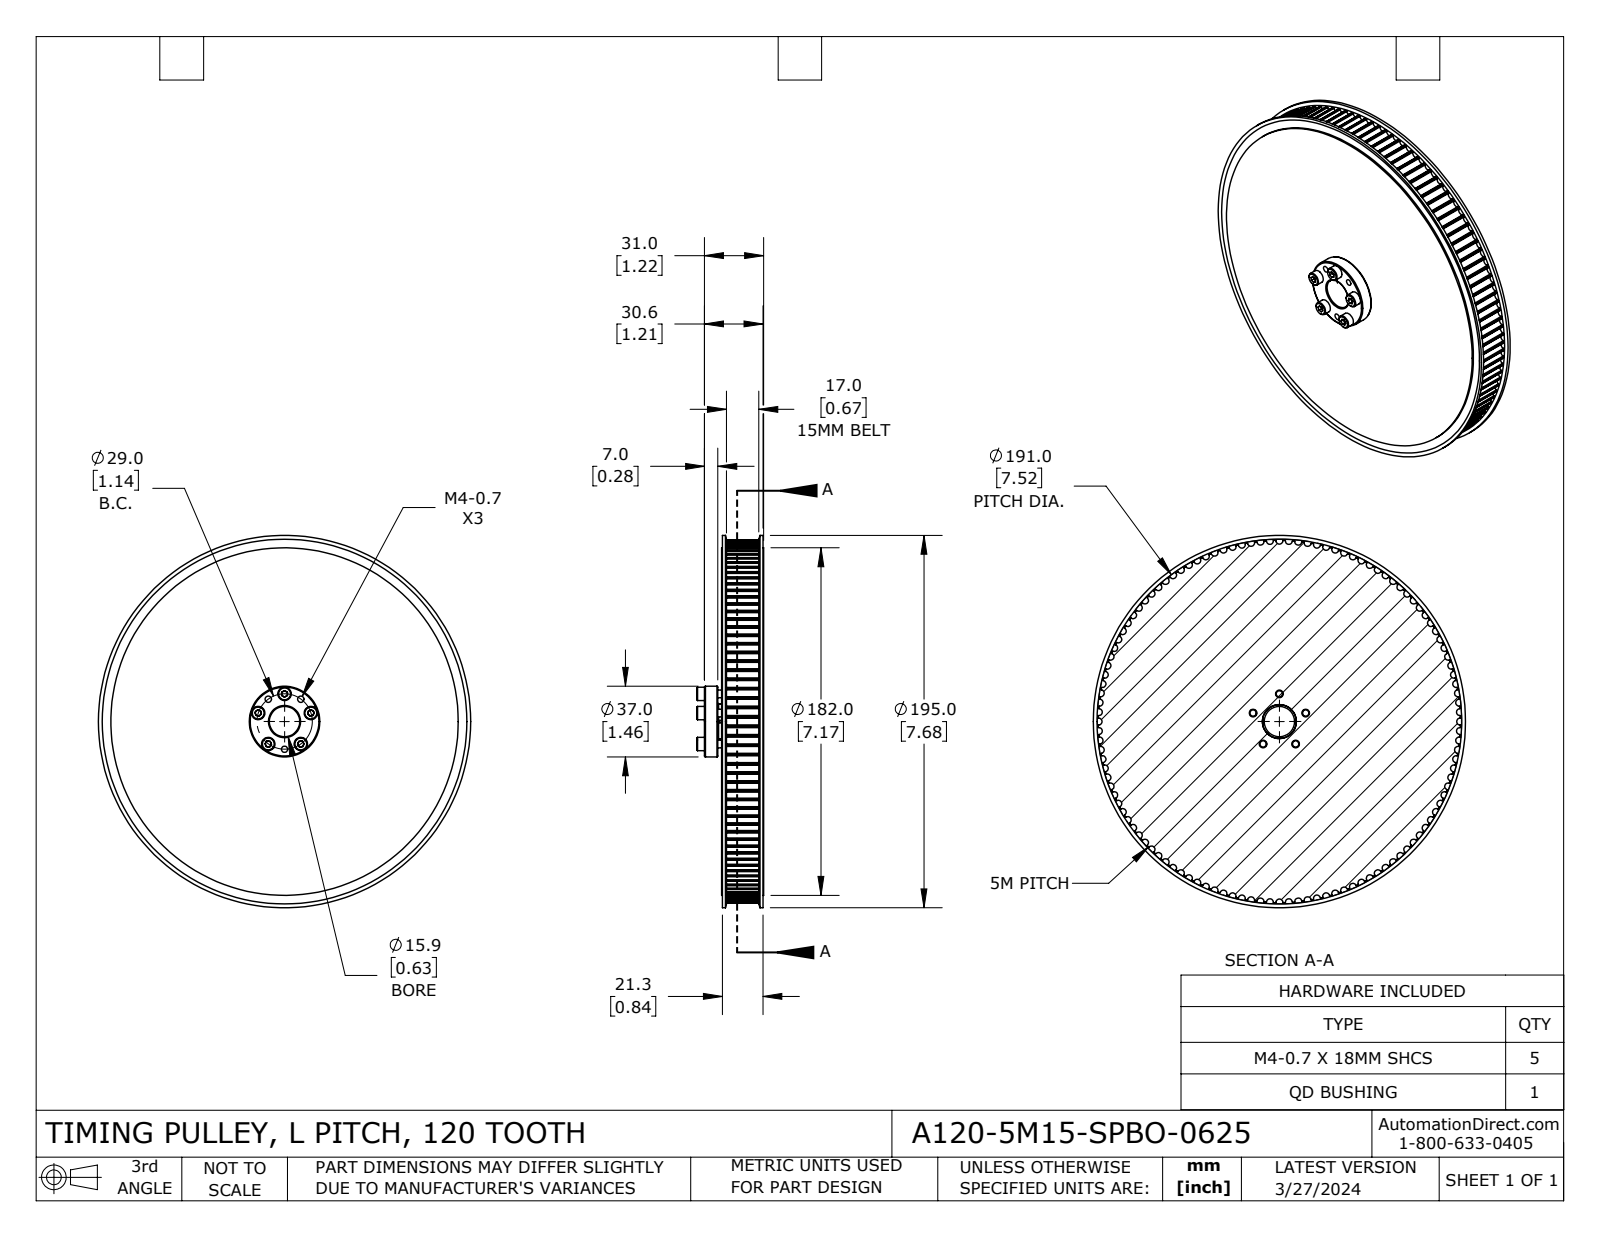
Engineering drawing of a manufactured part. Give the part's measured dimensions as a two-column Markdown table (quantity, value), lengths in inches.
| quantity | value |
| --- | --- |
| part name | A120-5M15-SPBO-0625 |
| STEP written by | SolidWorks 2021 (CONFIG_CONTROL_DESIGN) |
| units | inches |
| bodies | 9 solids, 830 faces (101 planar, 663 cylindrical, 66 other) |
| overall size | 7.677 × 7.677 × 1.378 |
| volume | 37.45 in³ |
| surface area | 155.7 in² |
| round holes (diameter × count) | 0.13 × 8, 0.177 × 5, 0.625 × 1, 0.727 × 1, 7.165 × 1 |
| round bosses / shafts (diameter × count) | 0.276 × 5, 0.157 × 5, 7.677 × 1, 1.457 × 1 |
| partial cylindrical surfaces (radius × count) | 0.012 × 240, 0.072 × 120, 3.737 × 1 |
| main face-to-face distances | 0.866, 0.098, 0.768, 0.035, 0.831, 0.063, 0.732, 0.669, 0.795, 0.354 |
| hole center spacings | 0.571, 1.086, 0.353, 0.924, 0.671, 1.142, 0.671 |
